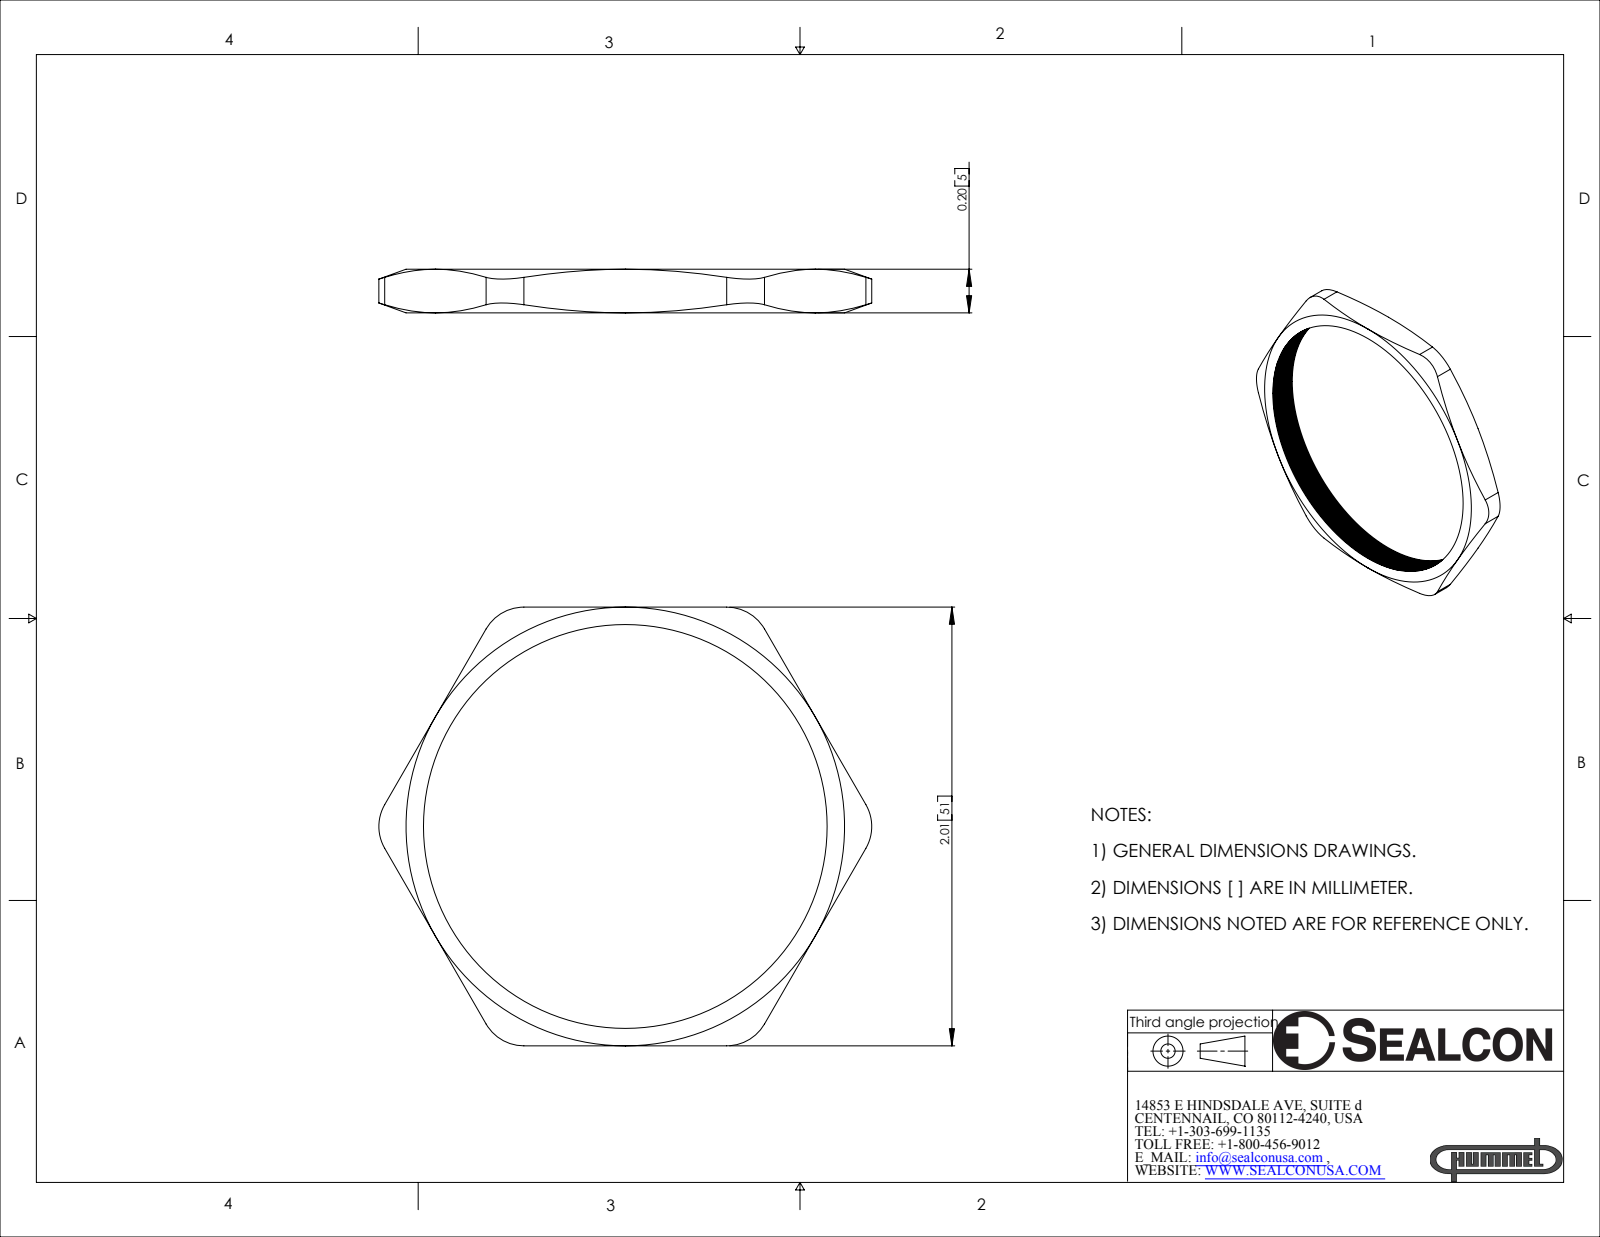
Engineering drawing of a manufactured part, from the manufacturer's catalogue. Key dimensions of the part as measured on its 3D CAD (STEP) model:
Part name (STEP PRODUCT): NP-36-BR
STEP written by: SolidWorks 2007 (CONFIG_CONTROL_DESIGN)
Units: inches
Bodies: 1 solid, 127 faces (8 planar, 7 cylindrical, 112 other)
Overall size (bounding box): 2.259 × 2.01 × 0.2
Volume: 0.136 in³ · Surface area: 5.027 in²
Partial cylindrical surfaces — rounded edges, fillets, slot ends (radius × count): R0.2 ×6
Main face-to-face distances: 2.01, 0.2
